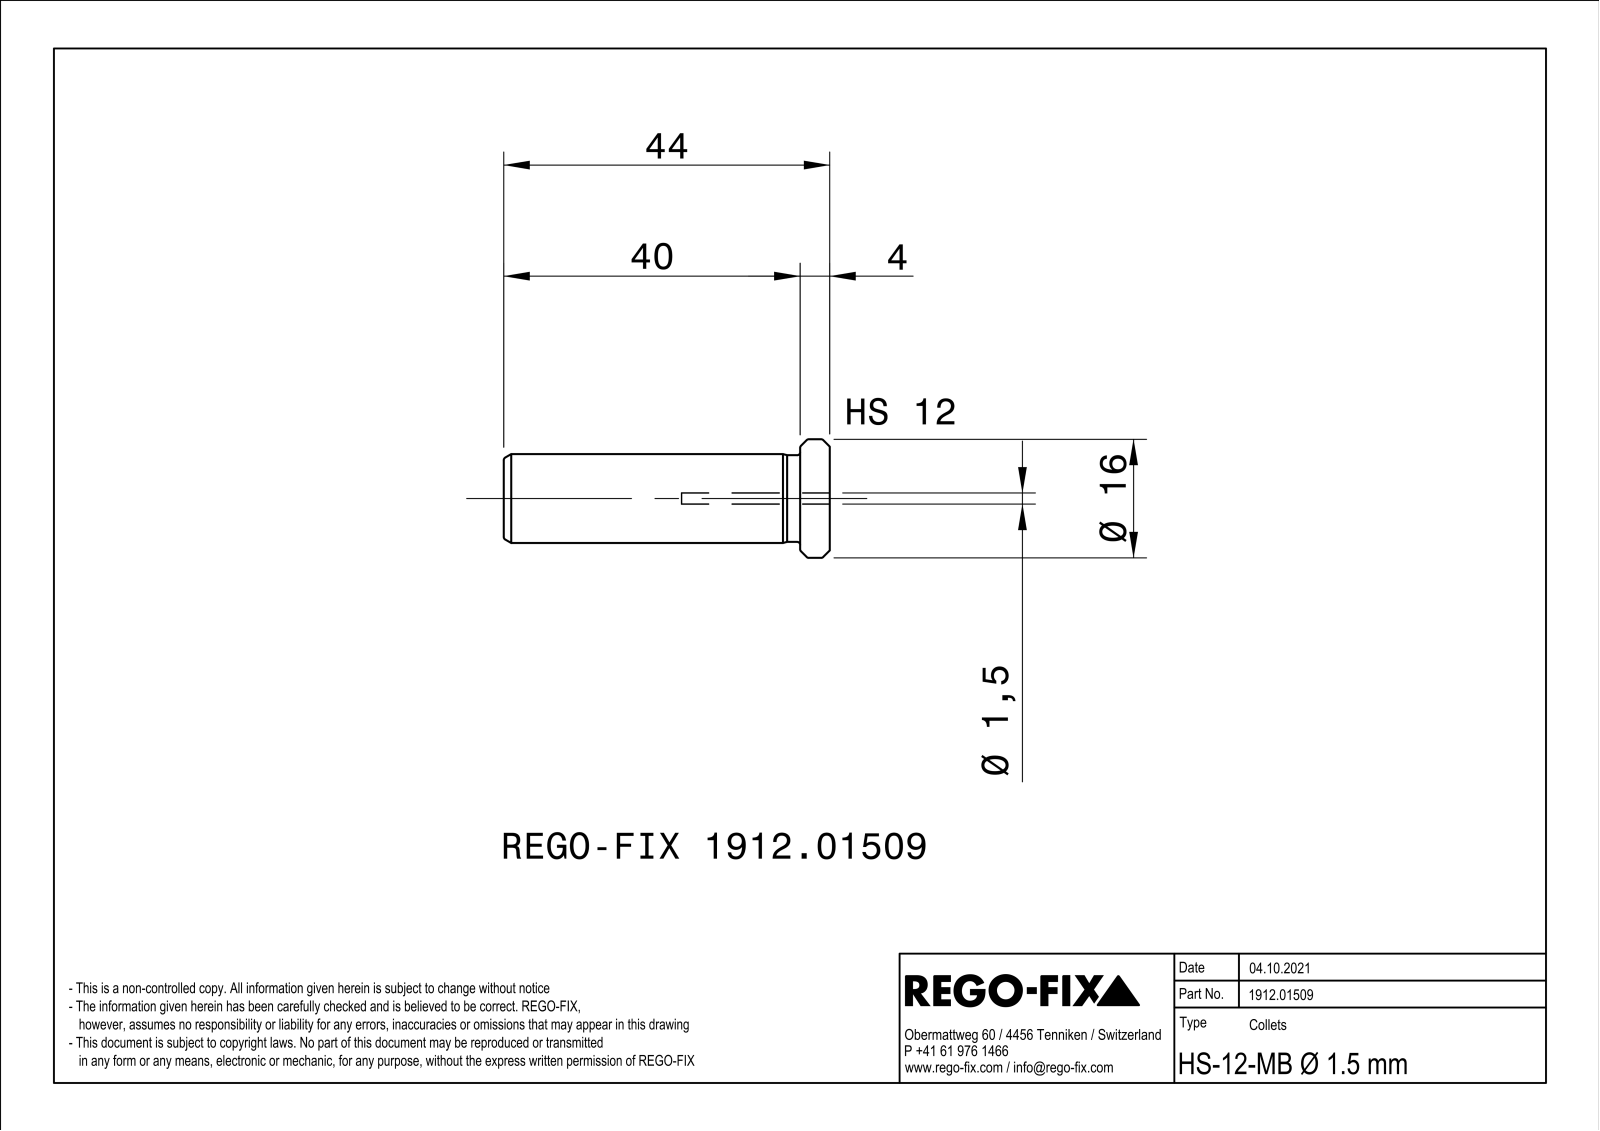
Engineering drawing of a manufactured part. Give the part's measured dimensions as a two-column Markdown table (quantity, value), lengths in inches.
| quantity | value |
| --- | --- |
| part name | NOCUT |
| STEP written by | SIEMENS PLM Software Solid Edge ST10 (AUTOMOTIVE_DESIGN) |
| units | inches |
| bodies | 1 solid, 67 faces (18 planar, 15 cylindrical, 34 other) |
| overall size | 1.732 × 0.63 × 0.629 |
| volume | 0.219 in³ |
| surface area | 5.546 in² |
| round holes (diameter × count) | 0.079 × 3, 0.059 × 1, 0.307 × 1, 0.323 × 1 |
| round bosses / shafts (diameter × count) | 0.63 × 1, 0.472 × 1, 0.461 × 1 |
| main face-to-face distances | 0.039, 1.732, 0.787, 0.945, 0.157, 0.63, 1.575 |
| hole center spacings | 0.18, 0.104, 0.104 |
